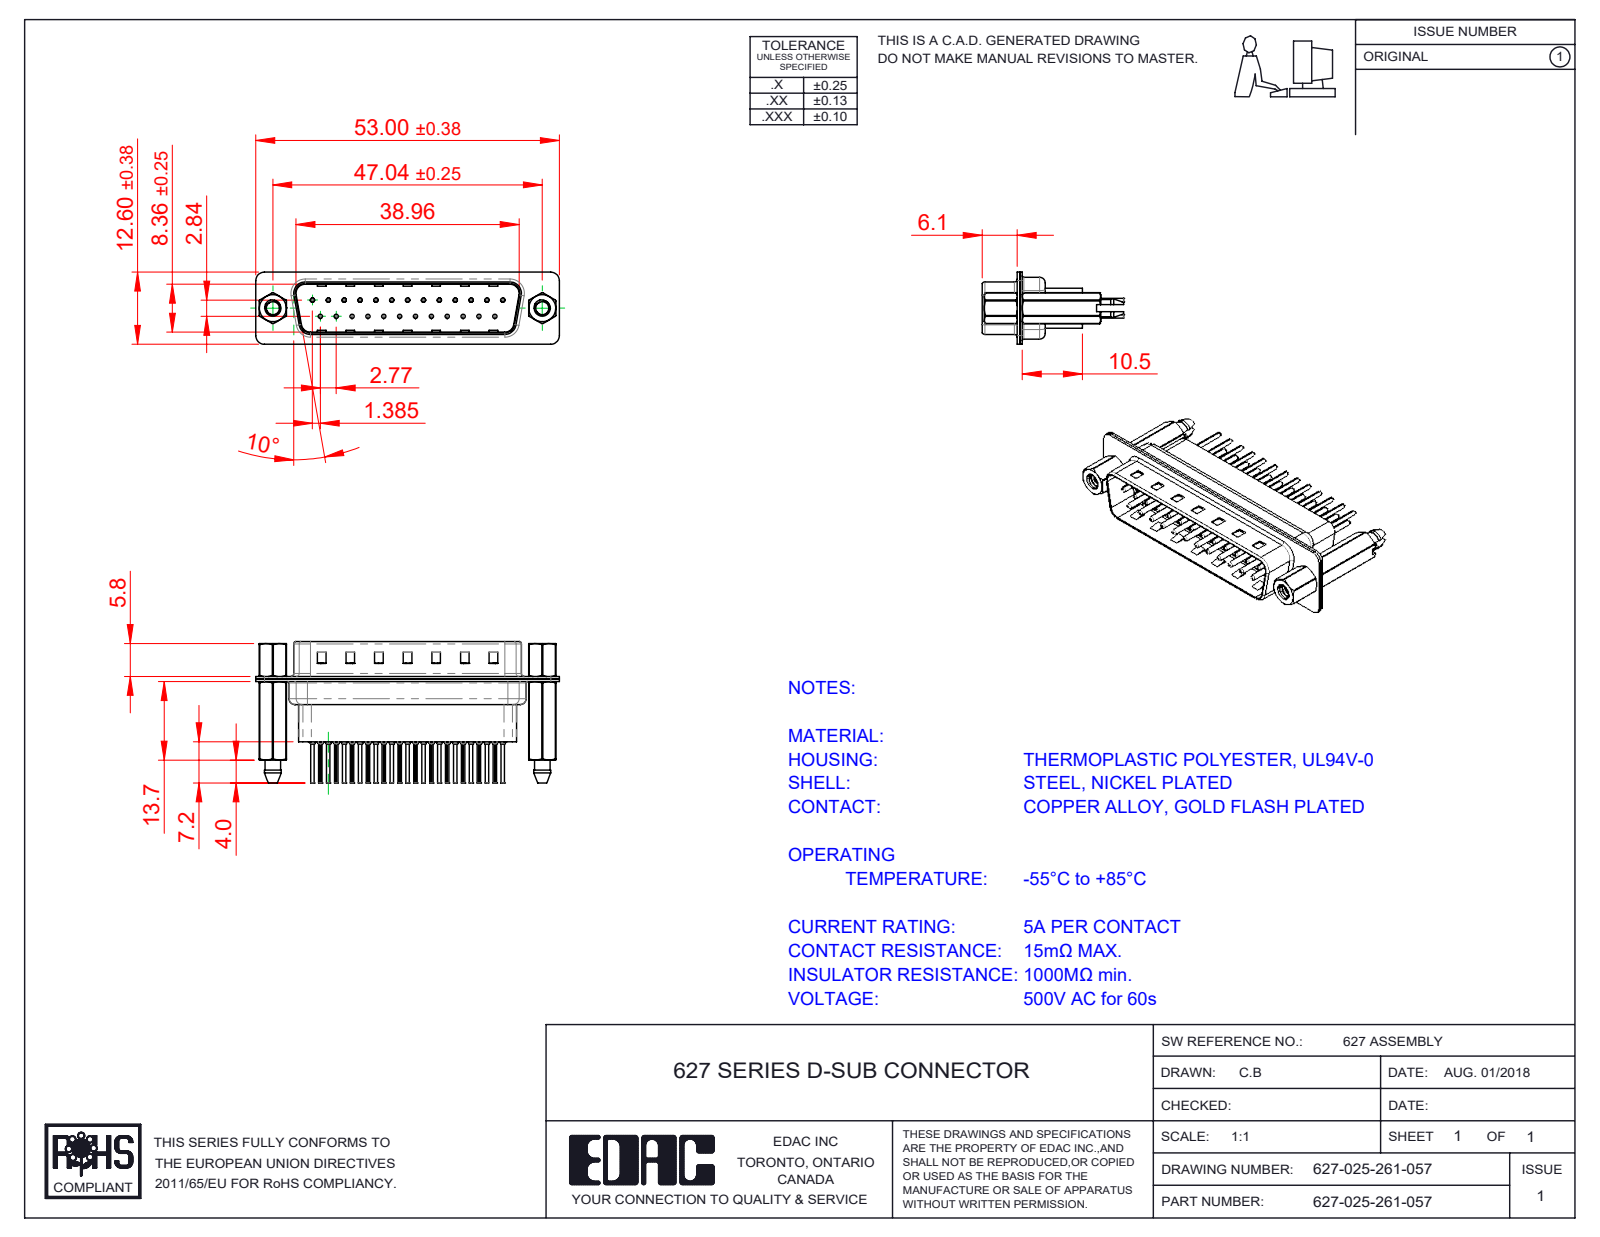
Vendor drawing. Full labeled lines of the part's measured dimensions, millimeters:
Part name (STEP PRODUCT): 627 Contact Row 2_61; 627 4-40 Hex Standoff; 627 Shell Front_25 Contacts; 627 Housing_25 HP (+4 more)
STEP written by: SolidWorks 2020 (CONFIG_CONTROL_DESIGN)
Units: millimetres
Bodies: 32 solids, 3060 faces (825 planar, 1200 cylindrical, 1035 other)
Overall size (bounding box): 53 × 24.6 × 12.6
Volume: 4 376 mm³ · Surface area: 11 253 mm²
Round holes (diameter × count): ⌀0.2 ×25, ⌀0.35 ×25, ⌀1.1 ×25, ⌀1.6 ×25, ⌀2.26 ×2, ⌀2.29 ×2, ⌀4 ×2, ⌀4.8 ×2
Round bosses / shafts (diameter × count): ⌀2 ×25, ⌀1.5 ×25, ⌀0.75 ×25, ⌀0.6 ×25, ⌀4.9 ×2, ⌀2.79 ×2
Partial cylindrical surfaces — rounded edges, fillets, slot ends (radius × count): R0.1 ×50, R1.5 ×18, R2 ×12, R1.6 ×10, R0.5 ×8, R0.25 ×4, R0.6 ×4, R0.65 ×4
Main face-to-face distances: 0.4, 0.45, 0.82, 9.58, 0.68, 7.68, 1.5, 0.9, 1.08, 8.08
Hole centre spacings: 3.16, 8.31, 2.77, 5.54, 11.08, 16.62, 5.03, 5.04
